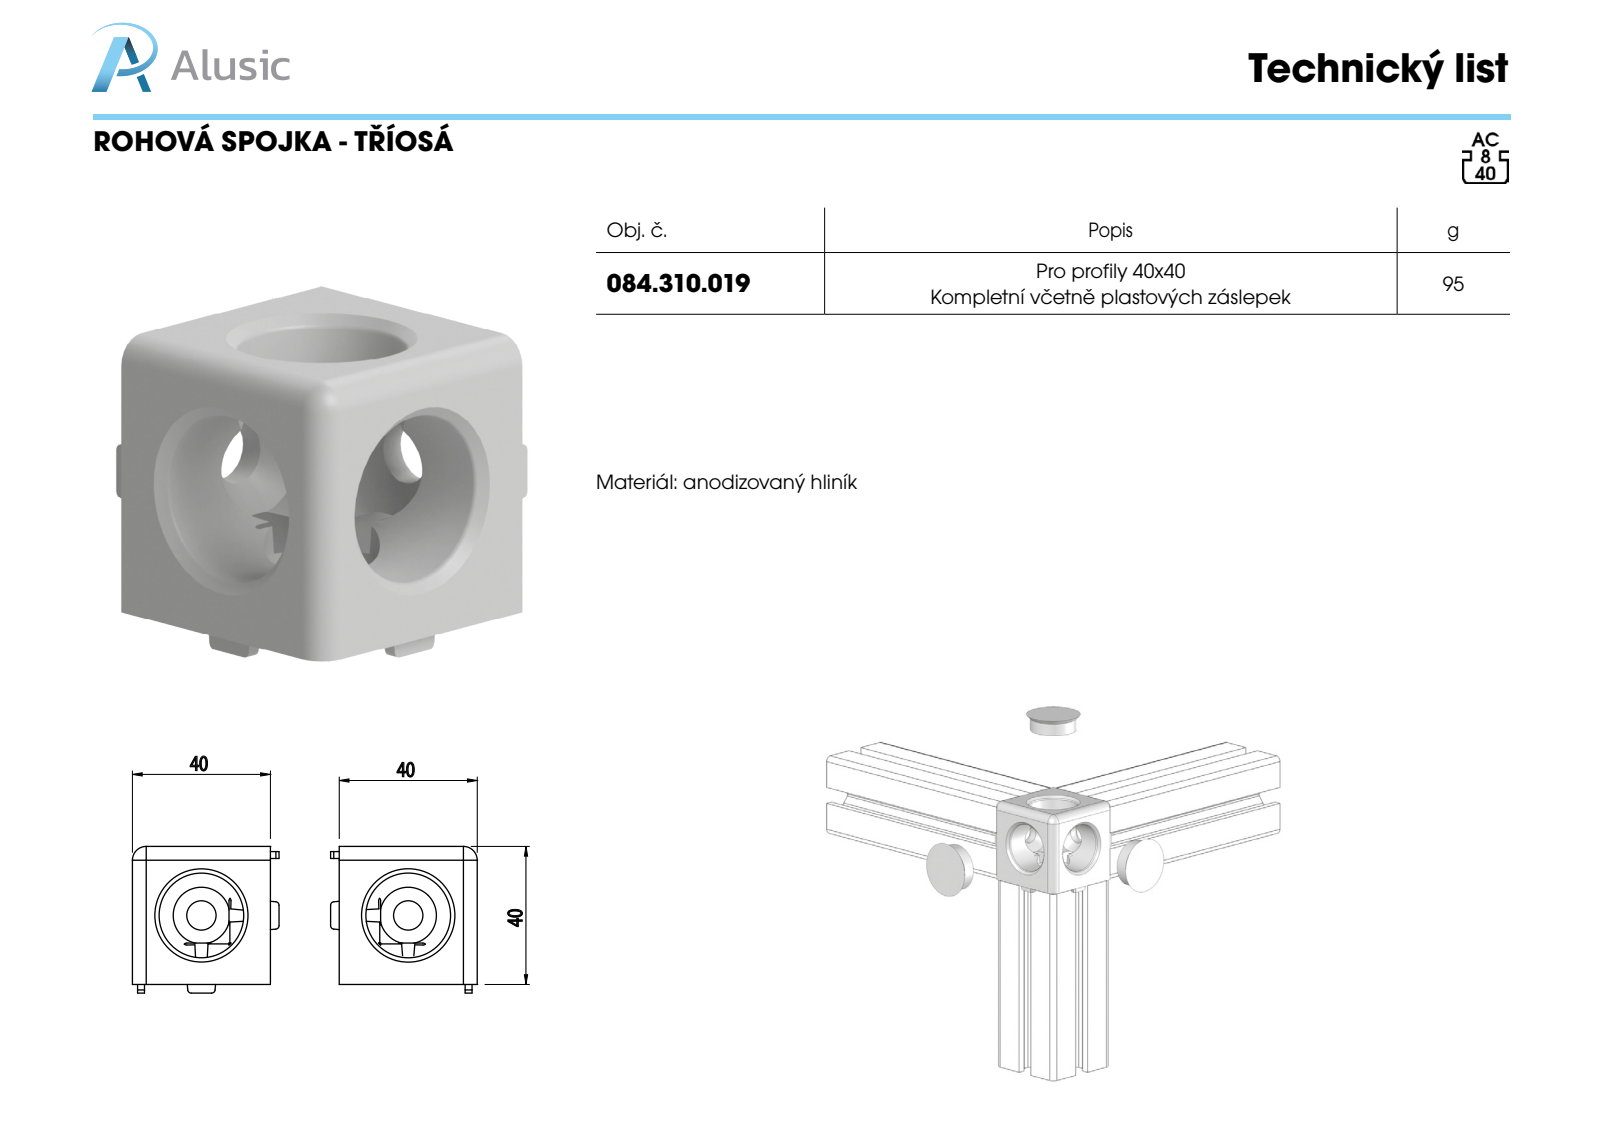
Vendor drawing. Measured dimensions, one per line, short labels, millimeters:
name: 084.310.019
written by: SolidWorks 2011 (CONFIG_CONTROL_DESIGN)
unit: mm
bodies: 1 solid, 115 faces (49 planar, 33 cylindrical, 33 other)
size: 42.5 × 42.5 × 42.5
volume: 34 237 mm³; area: 12 421 mm²
holes: 3× ⌀8.5
rounds: 24× R1, 3× R4
face distances: 40, 14.75, 25.25, 28, 12, 13.25, 2.75, 10.5, 1.5, 23.75
